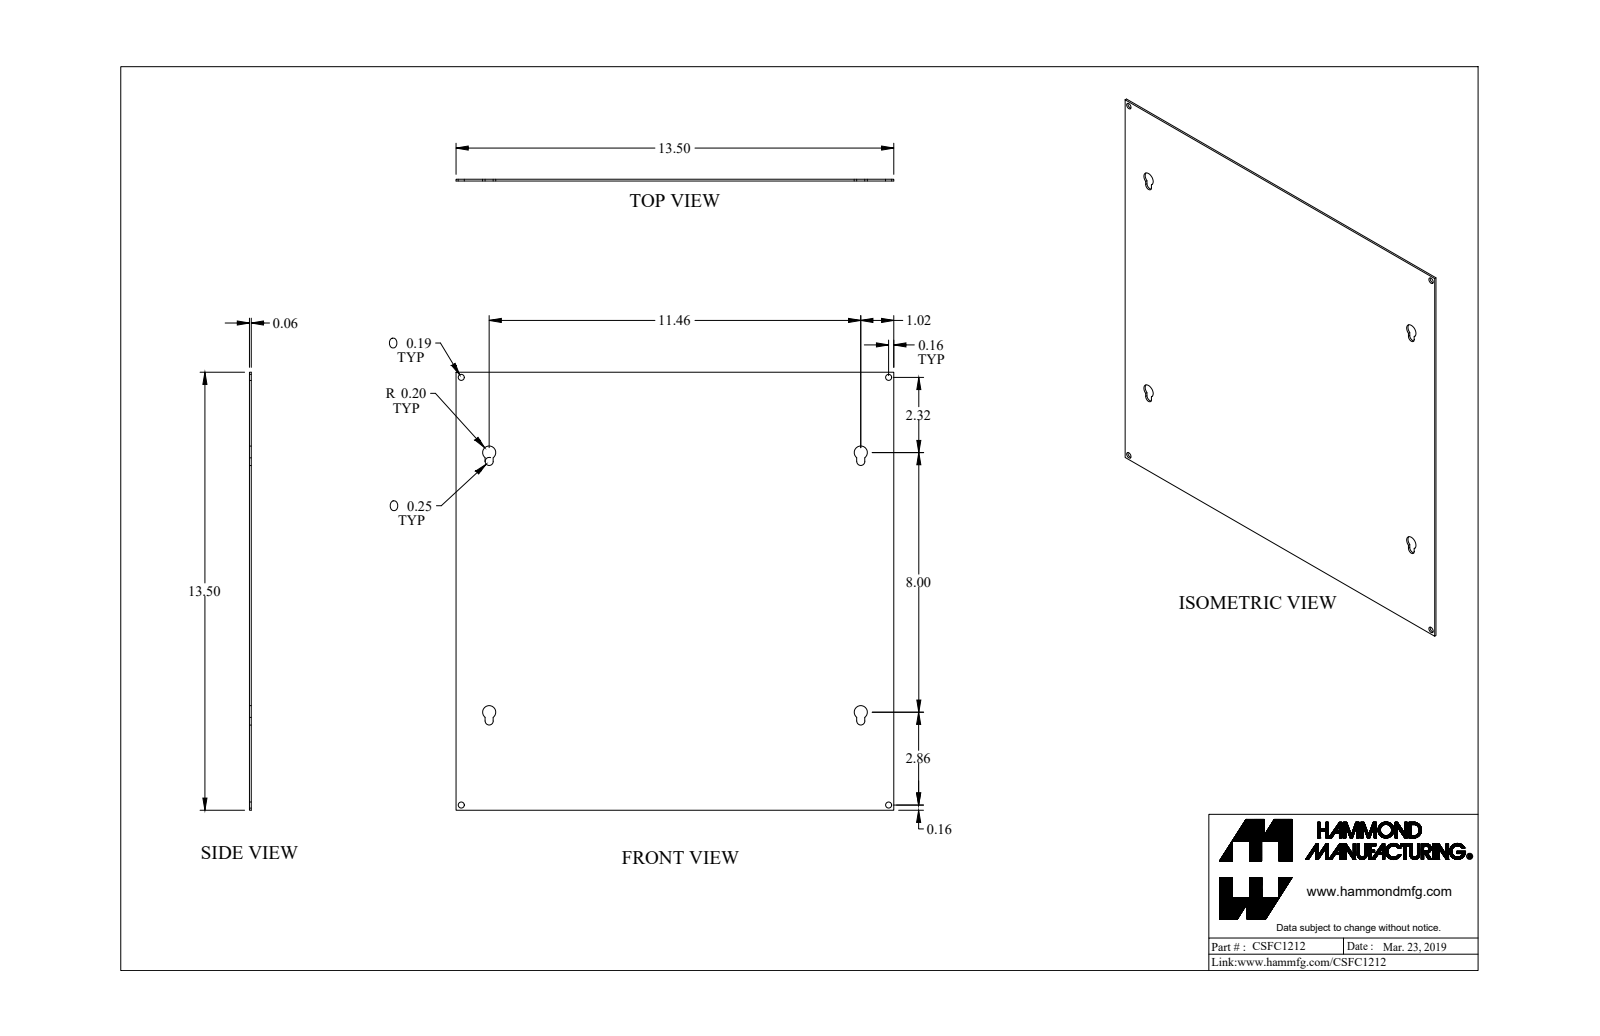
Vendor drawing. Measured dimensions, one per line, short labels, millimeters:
name: CSFC1212_Default
written by: SolidWorks 2019 (CONFIG_CONTROL_DESIGN)
unit: mm
bodies: 1 solid, 38 faces (14 planar, 24 cylindrical, 0 other)
size: 342.9 × 342.9 × 1.4
volume: 169 400 mm³; area: 236 500 mm²
holes: 4× ⌀4.8
rounds: 4× R3.2, 4× R5.2
face distances: 1.4, 342.9, 22.7, 29.1, 313.8, 320.2, 291.1, 6.4, 297.4, 284.7
hole spacings: 334.8, 473.5
